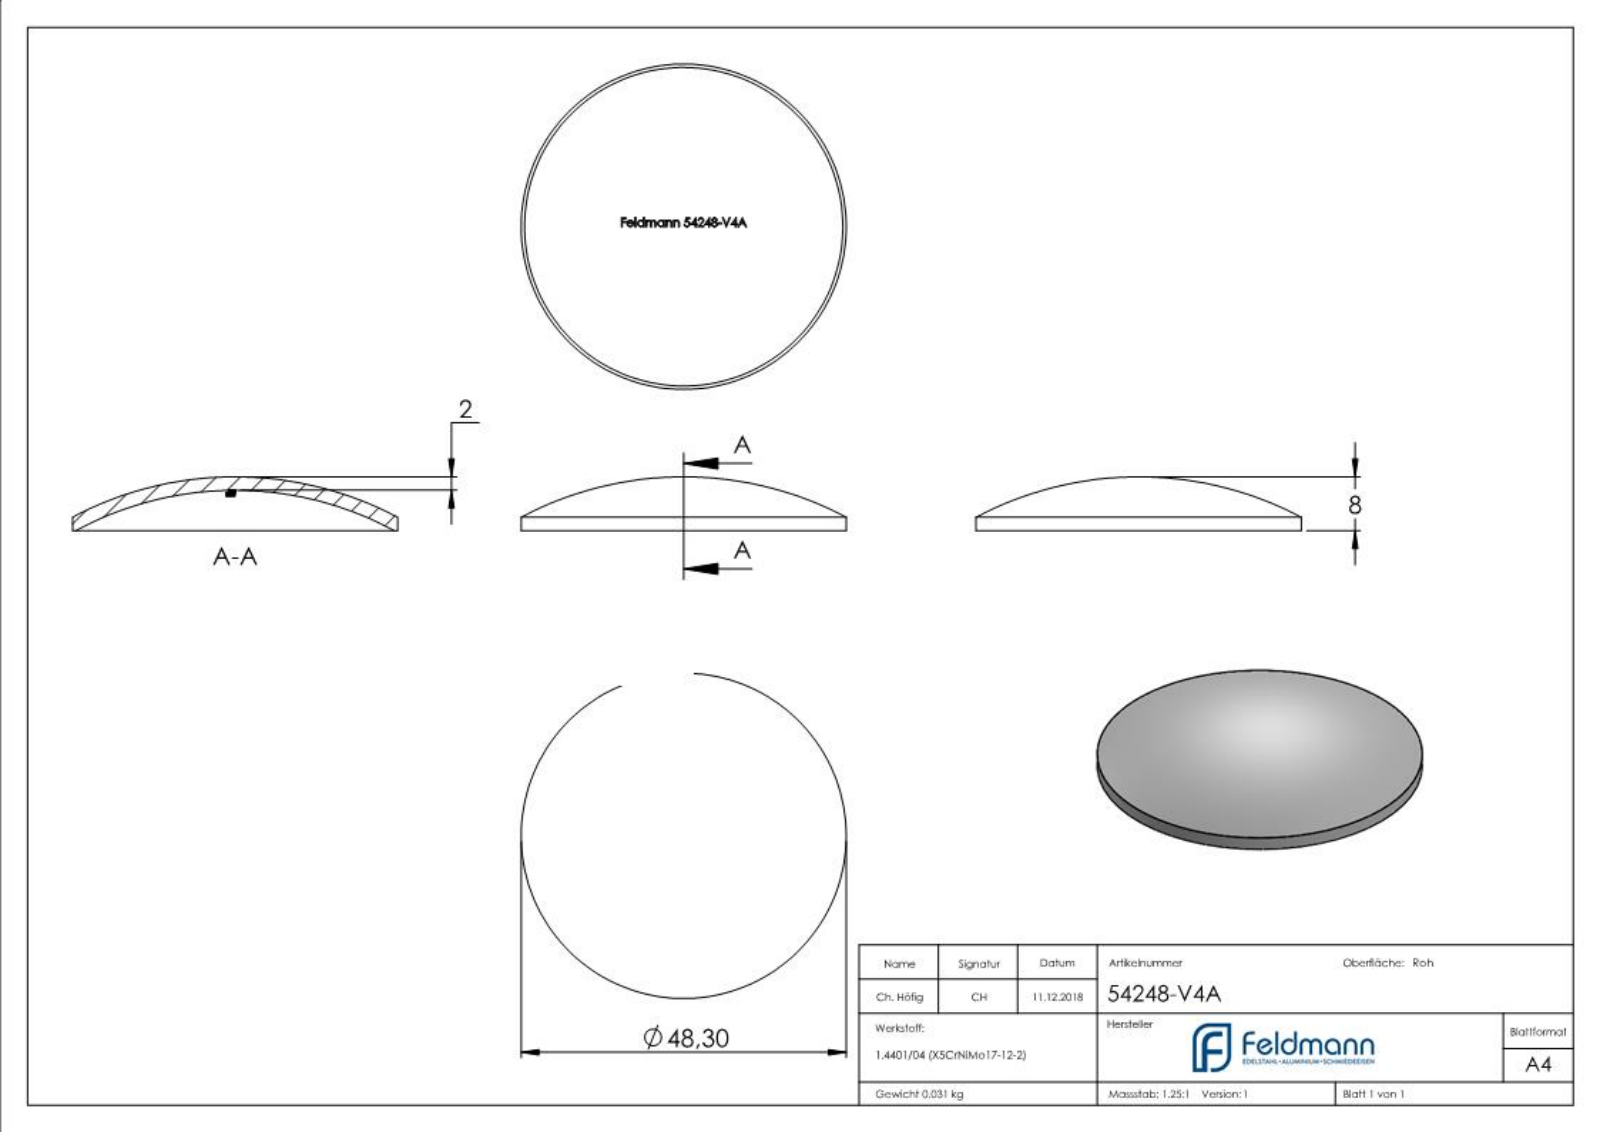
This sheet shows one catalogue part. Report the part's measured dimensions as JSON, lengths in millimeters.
{"part_name": "54248-V4A", "step_written_by": "SolidWorks 2015 (CONFIG_CONTROL_DESIGN)", "units": "millimeters", "bodies": {"solids": 1, "faces": 251, "planar": 128, "cylindrical": 2, "other": 121}, "overall_size": [48.3, 48.3, 8], "volume_mm3": 3890, "surface_area_mm2": 4204, "round_bosses_or_shafts": [[48.3, 1]], "face_to_face_distances": [0.44, 2.97, 0.39, 0.88, 2.01, 0.31, 1.26, 10.96, 5.97, 1.65]}
